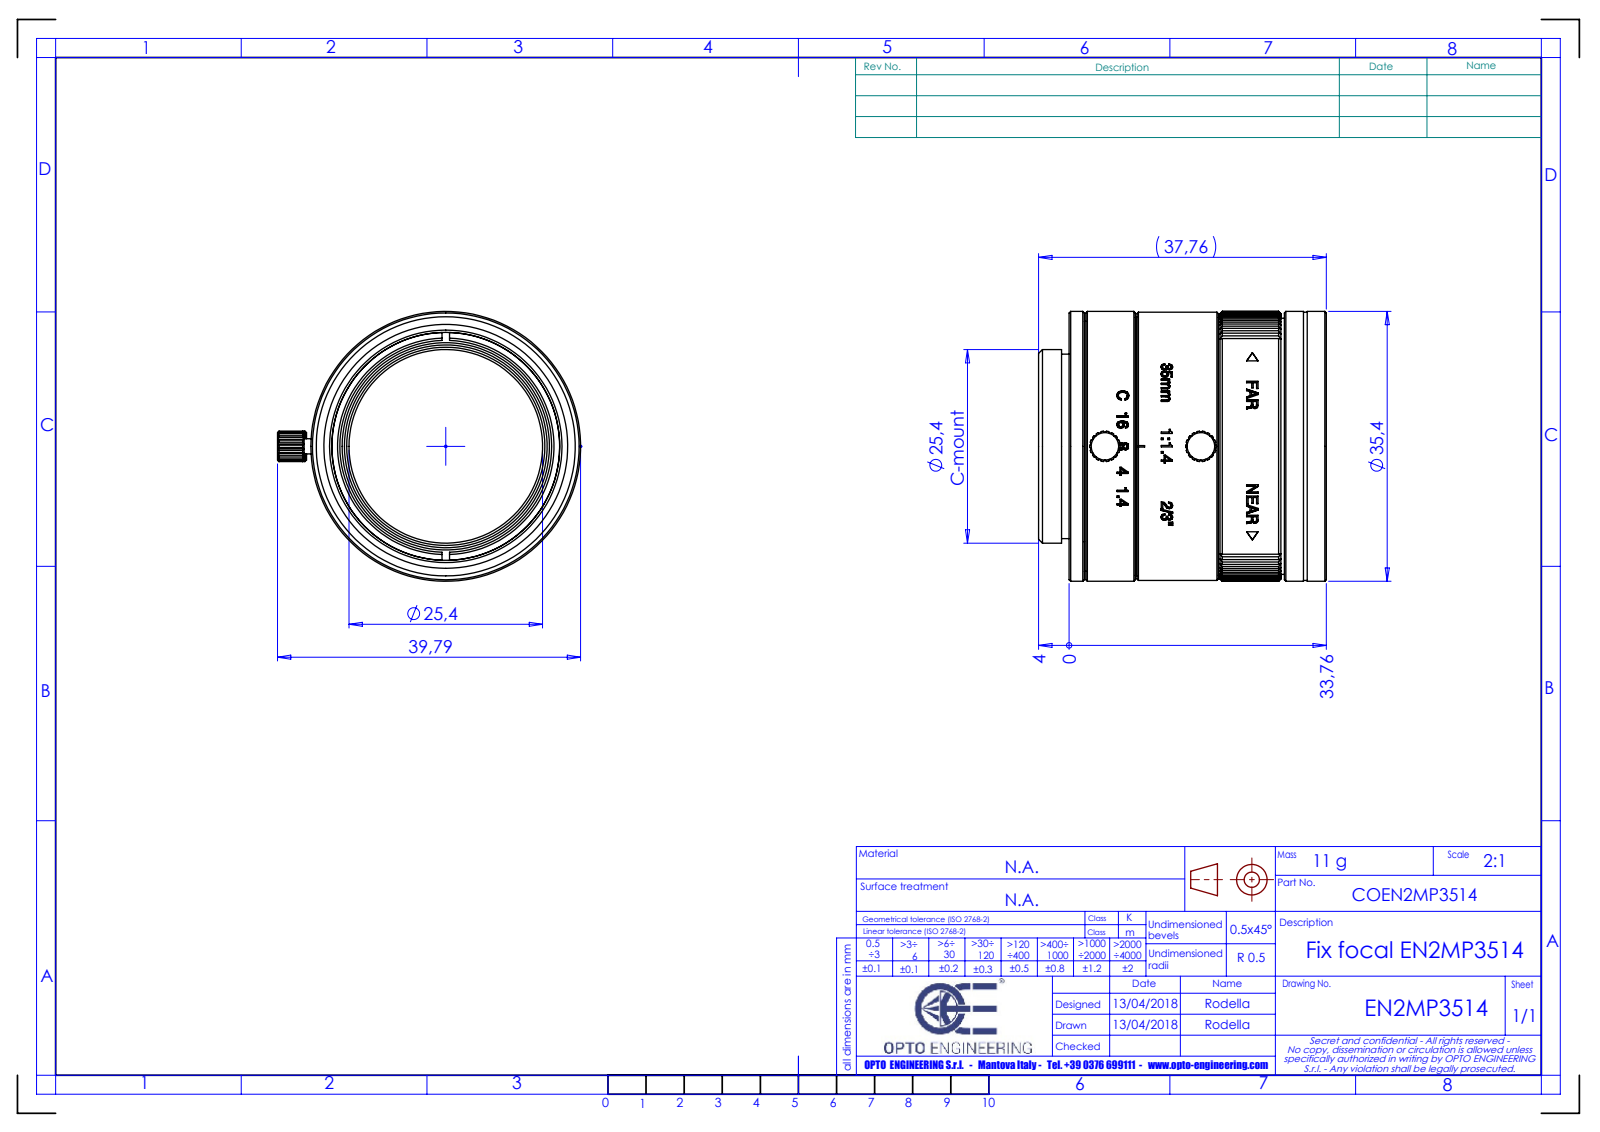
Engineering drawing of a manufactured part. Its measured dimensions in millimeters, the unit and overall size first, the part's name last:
Units: millimetres
Overall size (bounding box): 39.79 × 37.76 × 35.4
Round holes (diameter × count): ⌀1.7 ×4, ⌀2 ×4, ⌀1.2 ×3, ⌀1.4 ×3, ⌀2.6 ×1, ⌀14 ×1, ⌀18.6 ×1, ⌀19.2 ×1, ⌀22.4 ×1, ⌀25.4 ×1, ⌀26 ×1, ⌀26.6 ×1
Round bosses / shafts (diameter × count): ⌀1 ×3, ⌀2 ×2, ⌀35.4 ×1, ⌀35.2 ×1, ⌀33.8 ×1, ⌀33.6 ×1, ⌀32.8 ×1, ⌀32 ×1
Partial cylindrical surfaces — rounded edges, fillets, slot ends (radius × count): R0.5 ×2, R1.5 ×2, R2 ×2, R0.76 ×1, R17.5 ×1, R17.54 ×1, R17.55 ×1, R17.65 ×1
Main face-to-face distances: 0.93, 2, 26.26, 0.5, 5.5, 25.58, 24.65, 7.5, 3.75, 4.68
Hole centre spacings: 12.6, 13.8, 23.9, 2.1, 5.5, 10.5, 16, 18.1
Volume: 11 123 mm³ · Surface area: 16 650 mm²
Bodies: 17 solids, 1544 faces (670 planar, 358 cylindrical, 516 other)
Part name (STEP PRODUCT): M1435MP-11_5_AF0; PRT0041_AF0; M1435MP-10_1_AF0; PRT0042_AF0 (+8 more)
STEP written by: PRO/ENGINEER BY PARAMETRIC TECHNOLOGY CORPORATION, 2011310 (AUTOMOTIVE_DESIGN)
